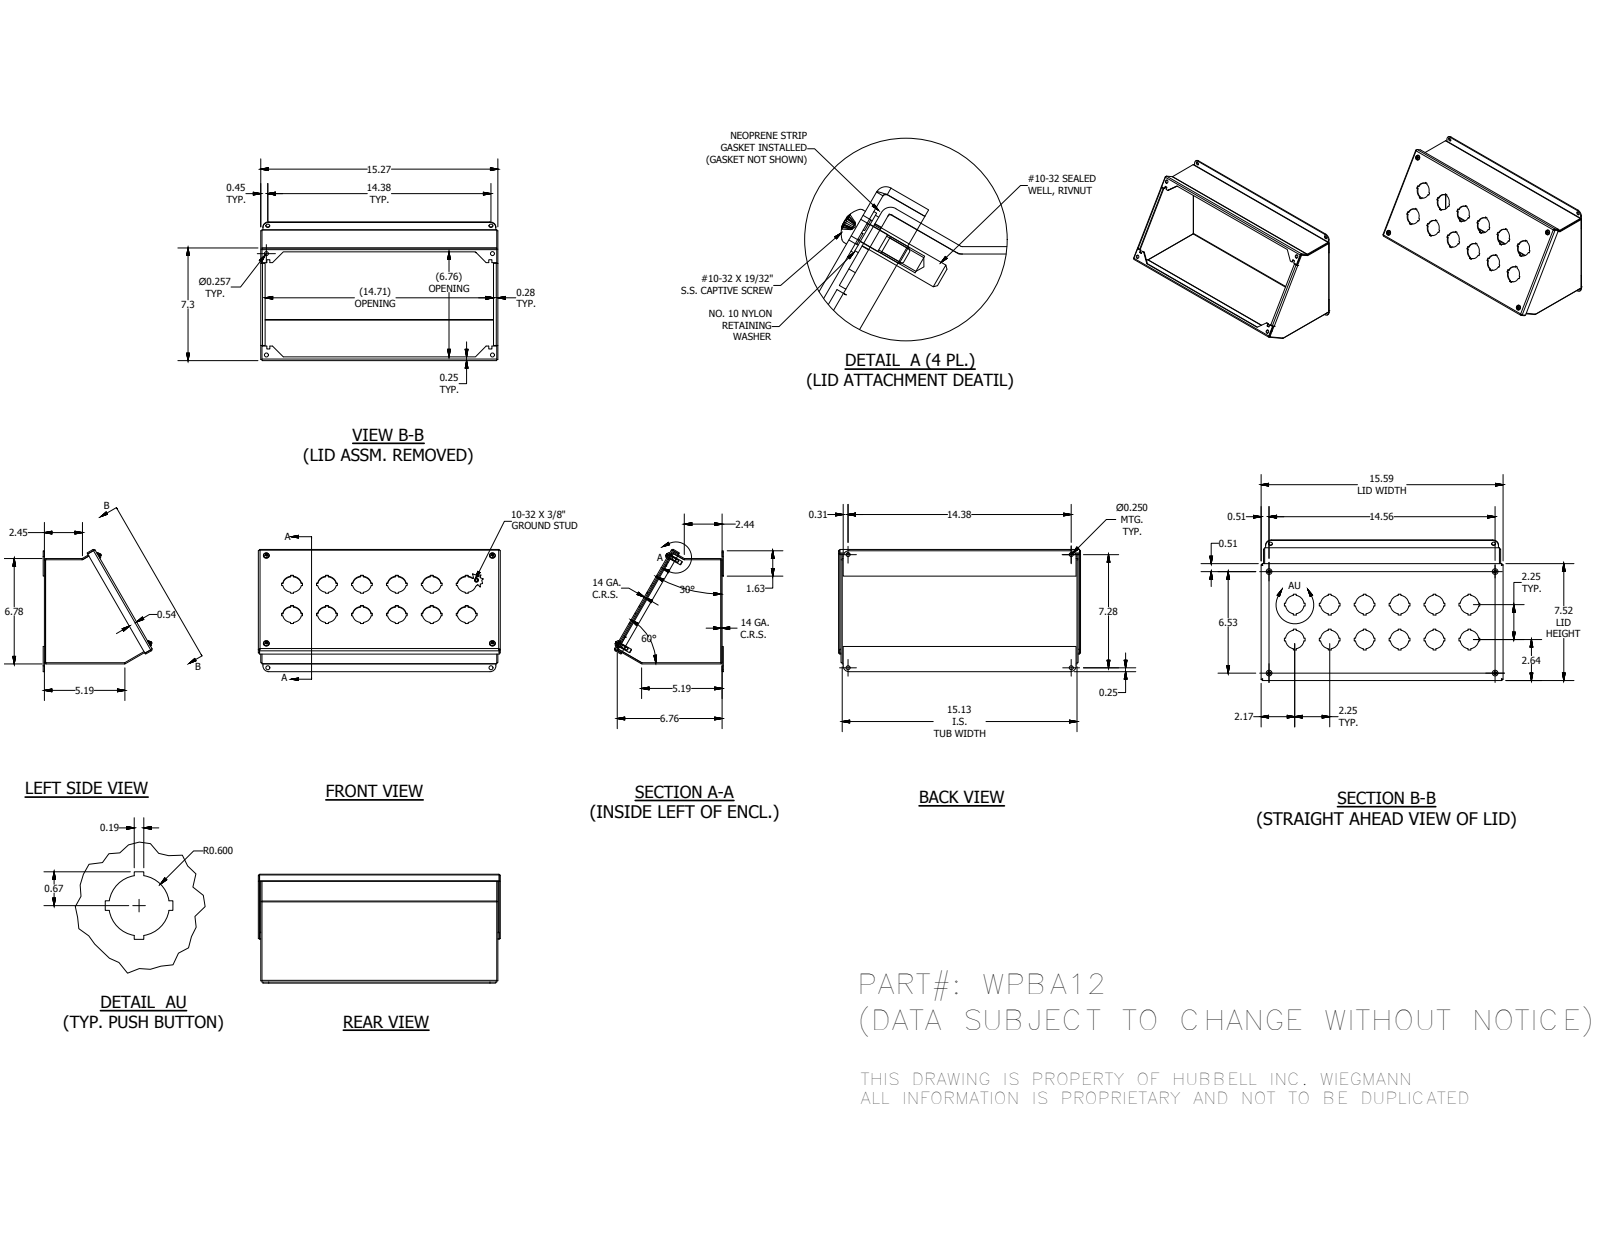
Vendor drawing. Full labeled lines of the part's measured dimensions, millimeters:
Part name (STEP PRODUCT): WPBA12BKP; WPBA2ROWEWPR; WPBA2ROWEWPL; 34984 (+6 more)
STEP written by: Autodesk Inventor 2014 (AUTOMOTIVE_DESIGN)
Units: millimetres
Bodies: 19 solids, 672 faces (435 planar, 138 cylindrical, 99 other)
Overall size (bounding box): 395.91 × 199.98 × 178.2
Volume: 615 011 mm³ · Surface area: 670 322 mm²
Round holes (diameter × count): ⌀30.48 ×12, ⌀3.96 ×4, ⌀4.98 ×4, ⌀6.35 ×4, ⌀6.53 ×4, ⌀7.06 ×4, ⌀7.14 ×4
Round bosses / shafts (diameter × count): ⌀4.83 ×5, ⌀11.51 ×4, ⌀10.31 ×4, ⌀9.47 ×4, ⌀6.3 ×4, ⌀6.35 ×1
Partial cylindrical surfaces — rounded edges, fillets, slot ends (radius × count): R0.79 ×12, R2.67 ×12, R2.27 ×4, R9.53 ×4
Main face-to-face distances: 1.88, 170.33, 3.76, 1.87, 168.45, 386.05, 172.21, 386.06, 387.93, 384.18
Hole centre spacings: 57.15, 80.82, 114.3, 127.79, 57.14, 171.45, 180.72, 68.42
